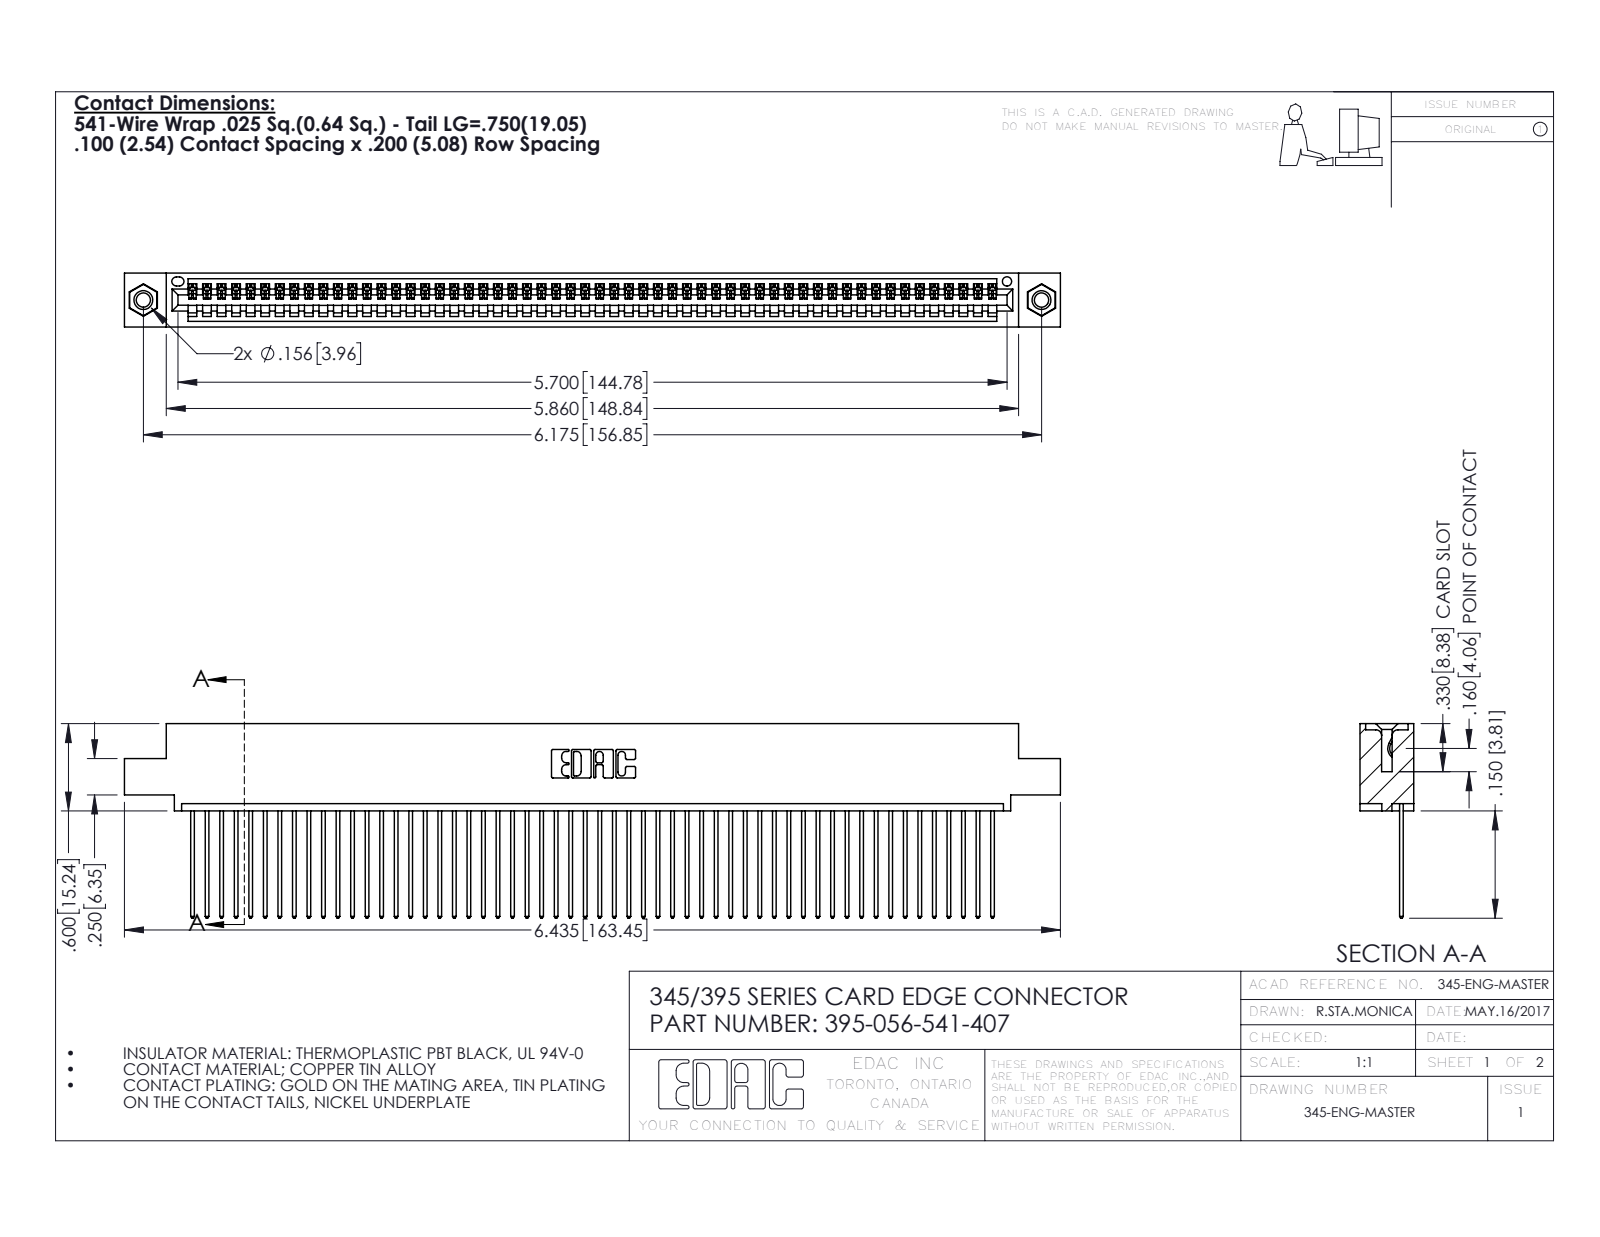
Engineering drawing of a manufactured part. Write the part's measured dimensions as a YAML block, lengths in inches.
part_name: "345-250-001_345-250-005-103; 345 Part_0.110 Offset - 0.156 Dia-TI; 395-056-541-407; 345-292-001_345-293-141"
step_written_by: "SolidWorks 2016 (CONFIG_CONTROL_DESIGN)"
units: inches
bodies: {solids: 59, faces: 3438, planar: 2356, cylindrical: 1066, other: 16}
overall_size: [6.435, 1.337, 0.37]
volume: 0.96
surface_area: 34.57
round_holes:
  - {diameter: 0.098, count: 2}
  - {diameter: 0.125, count: 2}
  - {diameter: 0.156, count: 2}
  - {diameter: 0.064, count: 1}
round_bosses_or_shafts:
  - {diameter: 0.155, count: 2}
partial_cylinders:
  - {radius: 0.006, count: 112}
  - {radius: 0.01, count: 112}
  - {radius: 0.01, count: 22}
  - {radius: 0.007, count: 6}
  - {radius: 0.031, count: 6}
  - {radius: 0.026, count: 3}
  - {radius: 0.031, count: 2}
  - {radius: 0.04, count: 2}
face_to_face_distances: [0.072, 0.298, 0.098, 0.272, 0.025, 0.37, 0.2, 0.225, 0.149, 0.072]
hole_center_spacings: [0.27, 5.939, 6.175]
